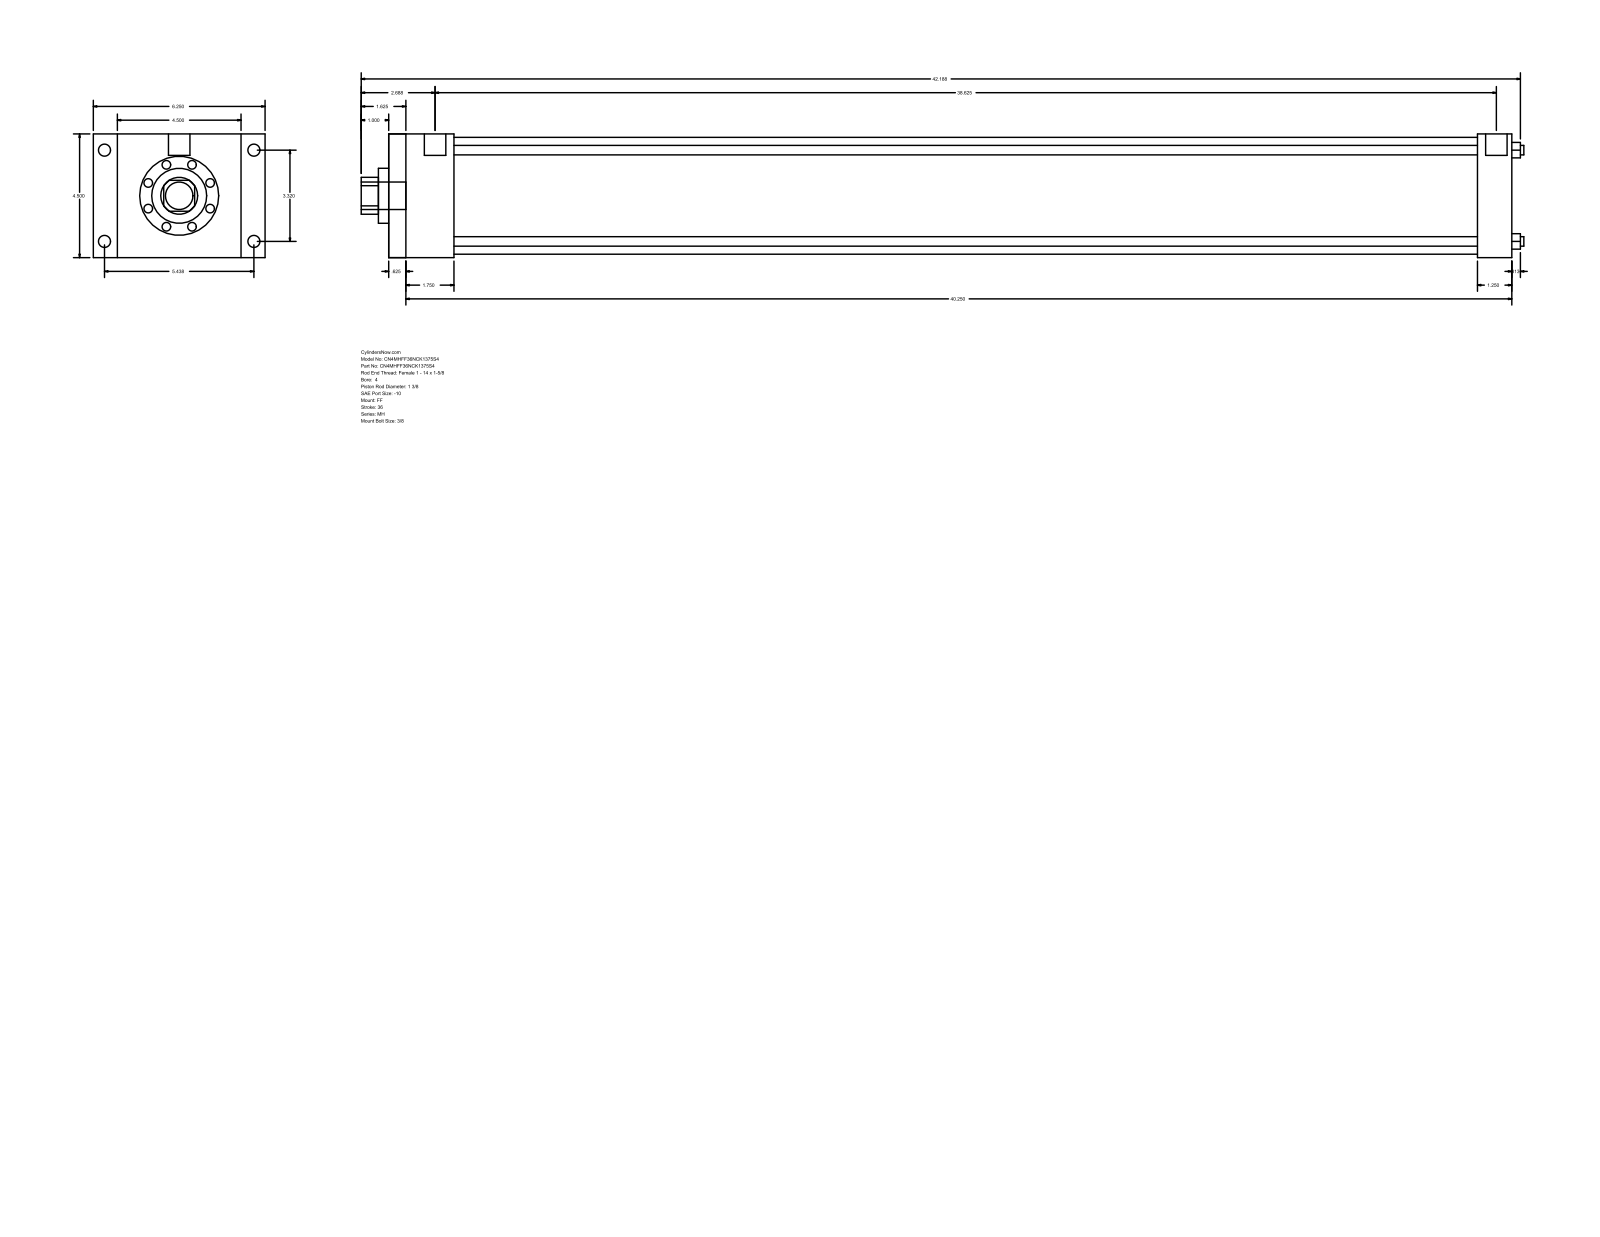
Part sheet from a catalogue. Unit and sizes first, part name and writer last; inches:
Units: inches
Overall size (bounding box): 42.313 × 6.25 × 4.5
Round holes (diameter × count): ⌀0.345 ×4, ⌀1.375 ×1, ⌀2 ×1, ⌀4.25 ×1
Round bosses / shafts (diameter × count): ⌀0.438 ×4, ⌀0.344 ×4, ⌀0.781 ×2, ⌀1 ×1
Partial cylindrical surfaces — rounded edges, fillets, slot ends (radius × count): R0.672 ×1
Main face-to-face distances: 4.5, 40.875, 0.625, 40.25, 2.375, 1.75, 38.5, 39.625, 39, 37.25
Hole centre spacings: 2.347, 3.32, 4.695
Bodies: 0 solids, 92 faces (64 planar, 28 cylindrical, 0 other)
Part name (STEP PRODUCT): MH_FF__0400_1.375
STEP written by: GSSL Pune (CONFIG_CONTROL_DESIGN)
